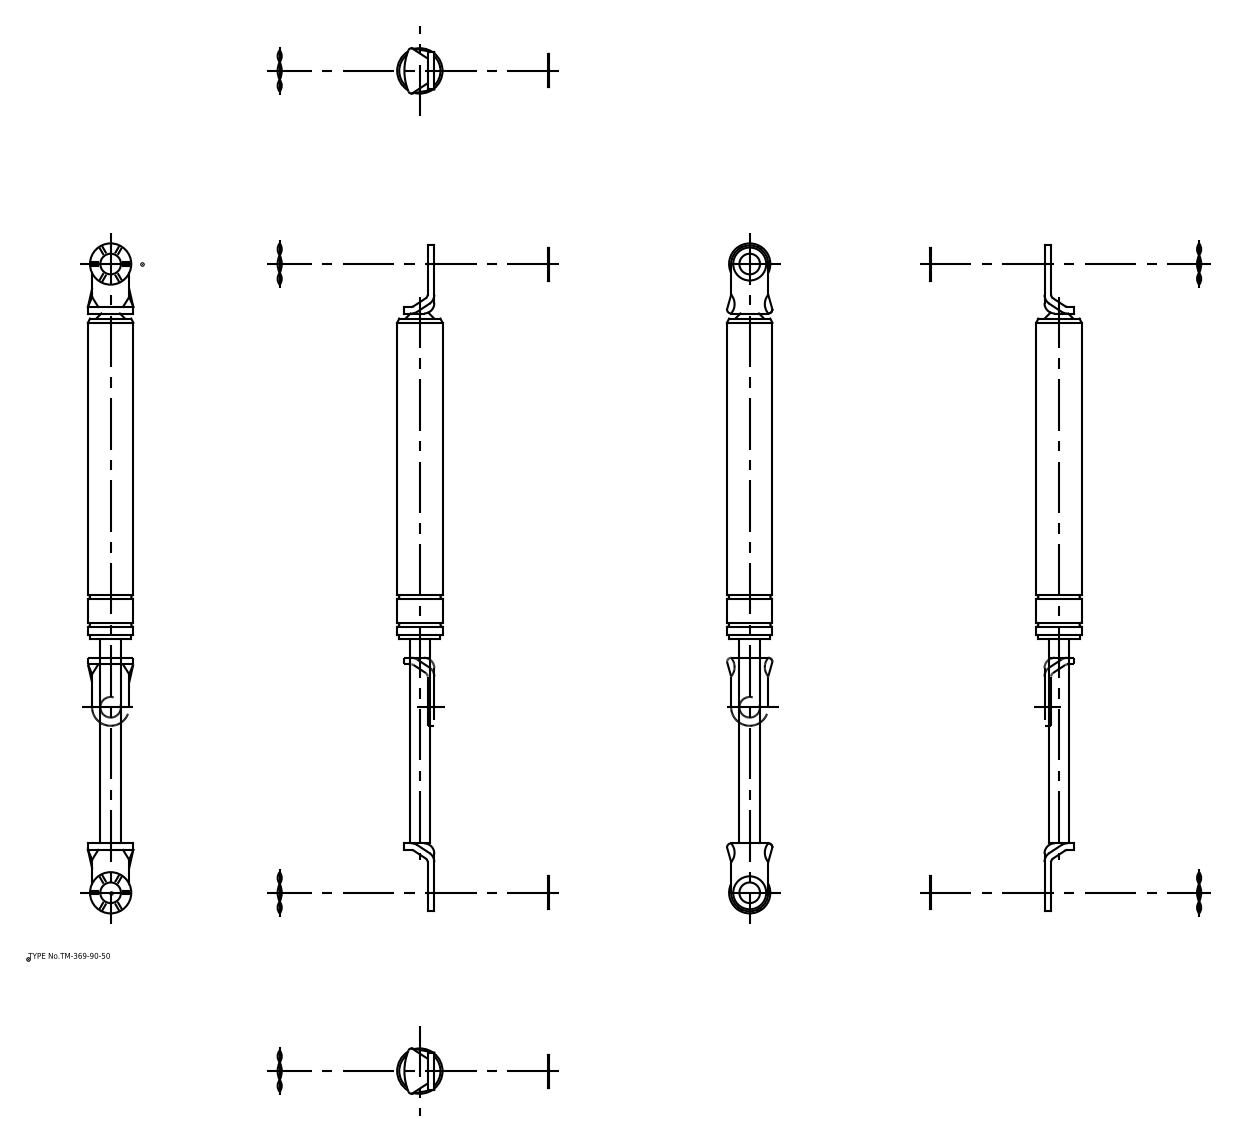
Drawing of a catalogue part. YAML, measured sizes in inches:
part_name: "ウェーブワッシャー; ワッシャー; 本体; 本体_div"
step_written_by: "spGate 16.7.1 (AUTOMOTIVE_DESIGN)"
units: inches
bodies: {solids: 6, faces: 95, planar: 43, cylindrical: 44, other: 8}
overall_size: [12.795, 0.886, 0.886]
volume: 4.429
surface_area: 31.49
round_holes:
  - {diameter: 0.394, count: 2}
round_bosses_or_shafts:
  - {diameter: 0.787, count: 3}
  - {diameter: 0.63, count: 2}
  - {diameter: 0.886, count: 1}
  - {diameter: 0.866, count: 1}
  - {diameter: 0.394, count: 1}
partial_cylinders:
  - {radius: 0.173, count: 2}
  - {radius: 0.197, count: 2}
  - {radius: 0.354, count: 2}
  - {radius: 1.036, count: 1}
face_to_face_distances: [0.126, 0.079, 0.205, 0.224, 10.244, 0.146, 0.02, 6.346, 4.024, 10.37]
hole_center_spacings: [12.008]
